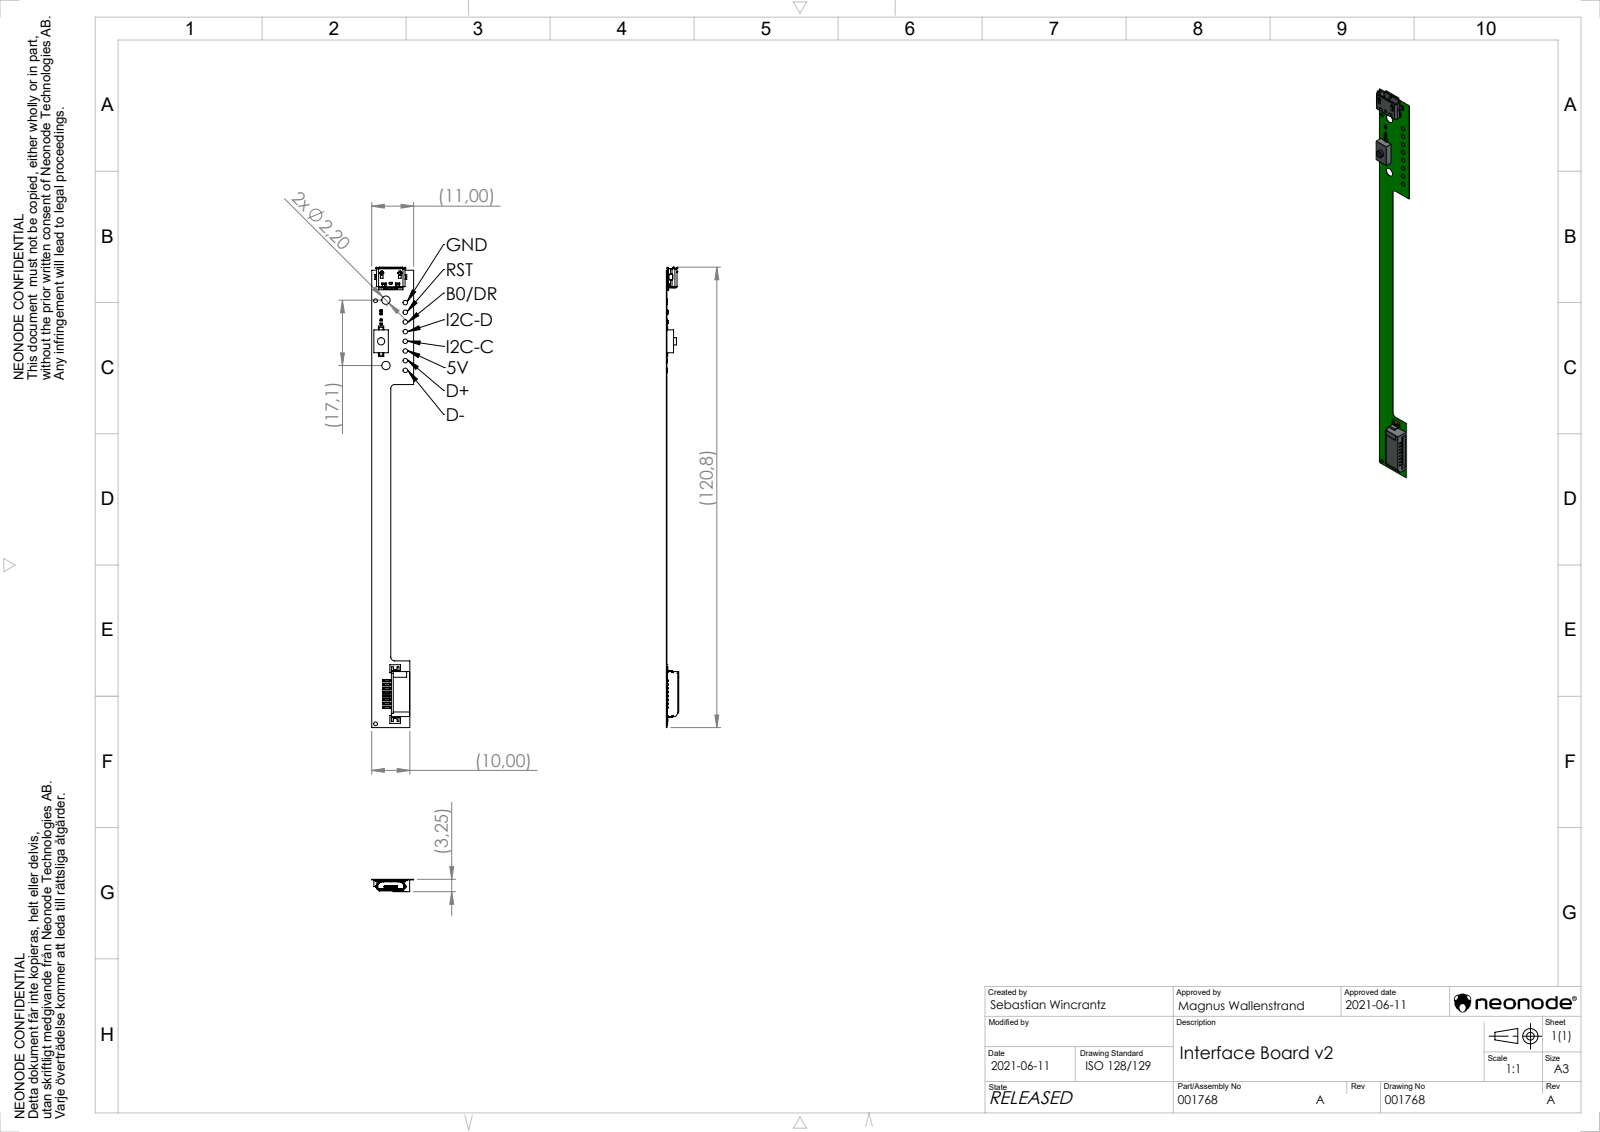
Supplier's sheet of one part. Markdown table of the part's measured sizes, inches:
| quantity | value |
| --- | --- |
| part name | FIDUCIAL_TOP^Pcb_Assembly_20PCB0001_A_001768; 001768_A; TESTPAD_1_5MM^Pcb_Assembly_20PCB0001_A_001768; CON_MOLEX_8N_P1MM_FLEX_527930870^Pcb_Assembly_20PCB0001_A_001768 (+6 more) |
| STEP written by | SolidWorks 2020 (CONFIG_CONTROL_DESIGN) |
| units | inches |
| bodies | 22 solids, 835 faces (615 planar, 208 cylindrical, 12 other) |
| overall size | 4.756 × 0.433 × 0.128 |
| volume | 0.008 in³ |
| surface area | 3.942 in² |
| round holes (diameter × count) | 0.087 × 2 |
| round bosses / shafts (diameter × count) | 0.047 × 8, 0.039 × 2, 0.075 × 1 |
| partial cylindrical surfaces (radius × count) | 0.008 × 36, 0.01 × 16, 0.006 × 10, 0.012 × 9, 0.022 × 8, 0.004 × 7, 0.005 × 4, 0.006 × 4 |
| main face-to-face distances | 0.026, 0.118, 0.018, 0.096, 0.085, 0.024, 0.02, 0.014, 0.079, 0.093 |
| hole center spacings | 0.675 |
